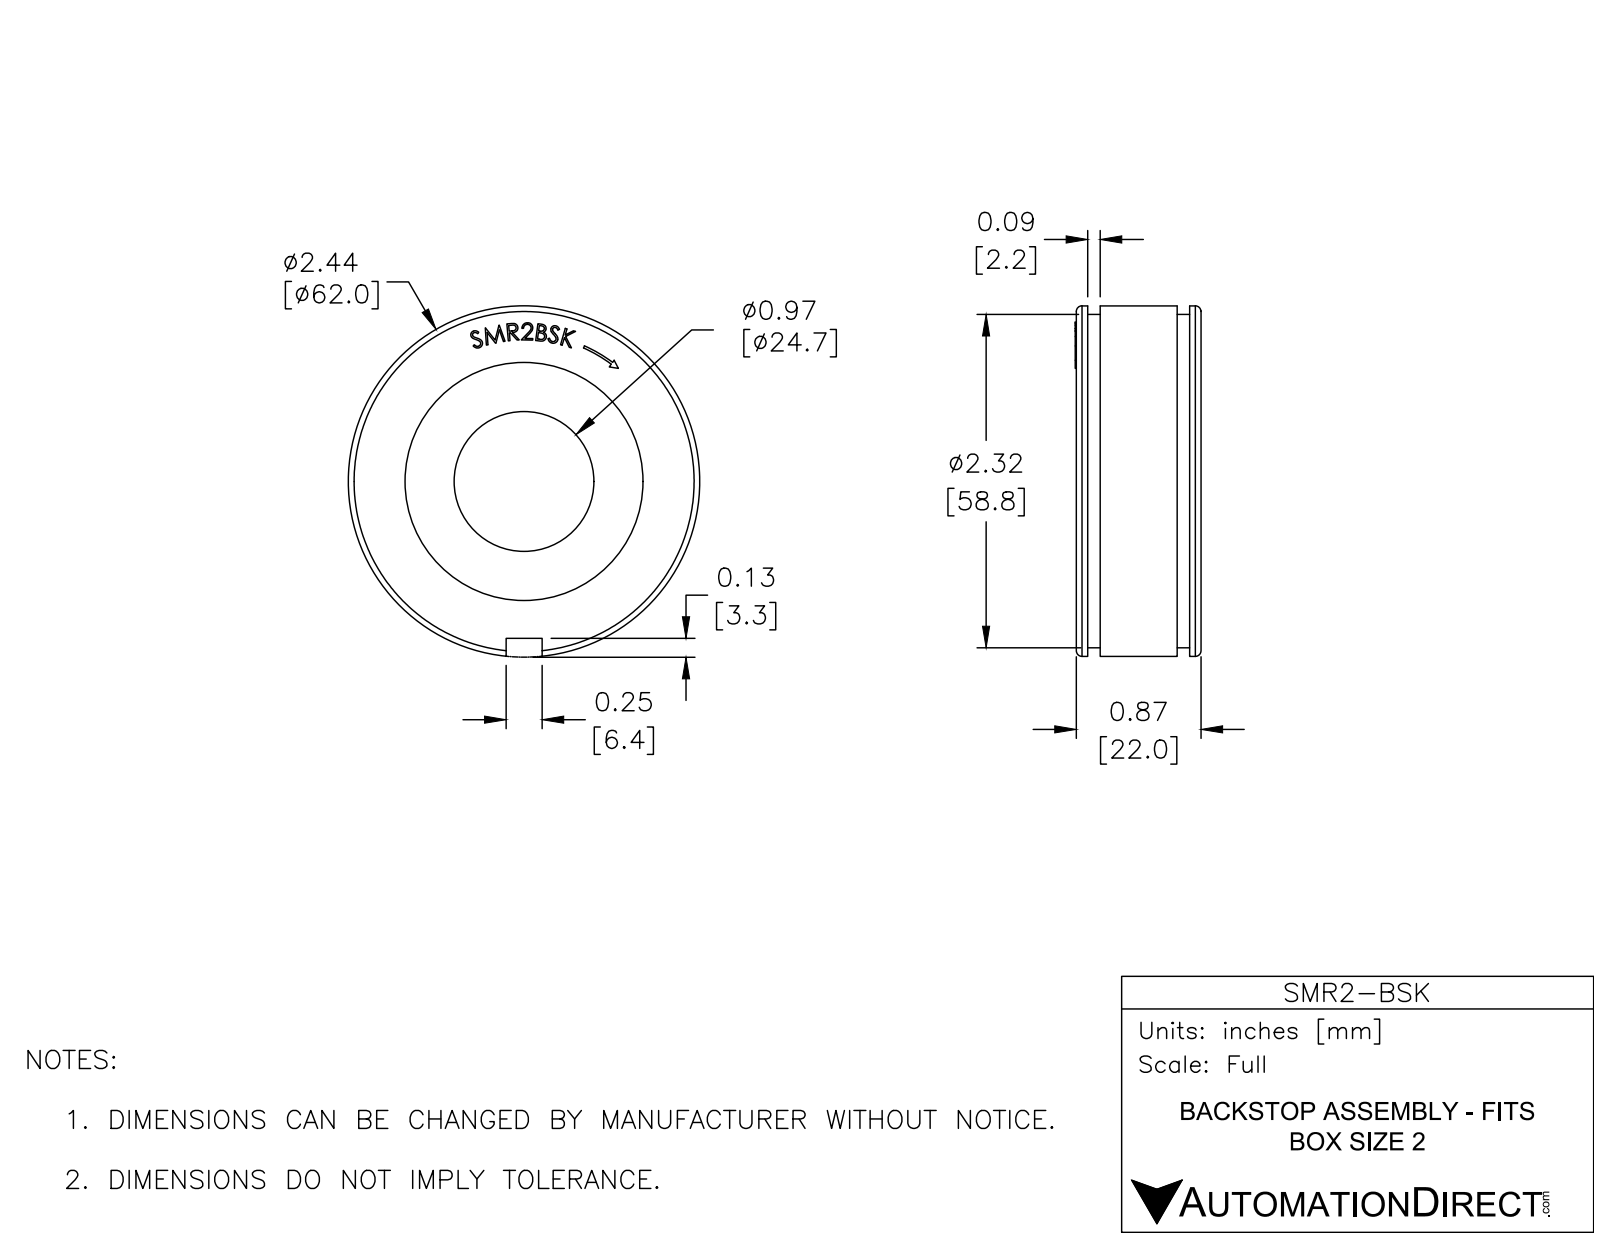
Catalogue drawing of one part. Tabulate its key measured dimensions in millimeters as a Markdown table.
| quantity | value |
| --- | --- |
| part name | SMR2-BSK |
| STEP written by | SolidWorks 2016 (AUTOMOTIVE_DESIGN) |
| units | millimeters |
| bodies | 1 solid, 160 faces (81 planar, 23 cylindrical, 56 other) |
| overall size | 62 × 61.8 × 22.2 |
| volume | 53 260 mm³ |
| surface area | 12 140 mm² |
| round holes (diameter × count) | 24.6 × 1, 42 × 1 |
| round bosses / shafts (diameter × count) | 62 × 1, 59 × 1 |
| partial cylindrical surfaces (radius × count) | 25.8 × 1, 26.2 × 1 |
| main face-to-face distances | 0.5, 21.5, 22, 21, 2.2, 2, 20, 1.5, 19.5, 4.2 |
